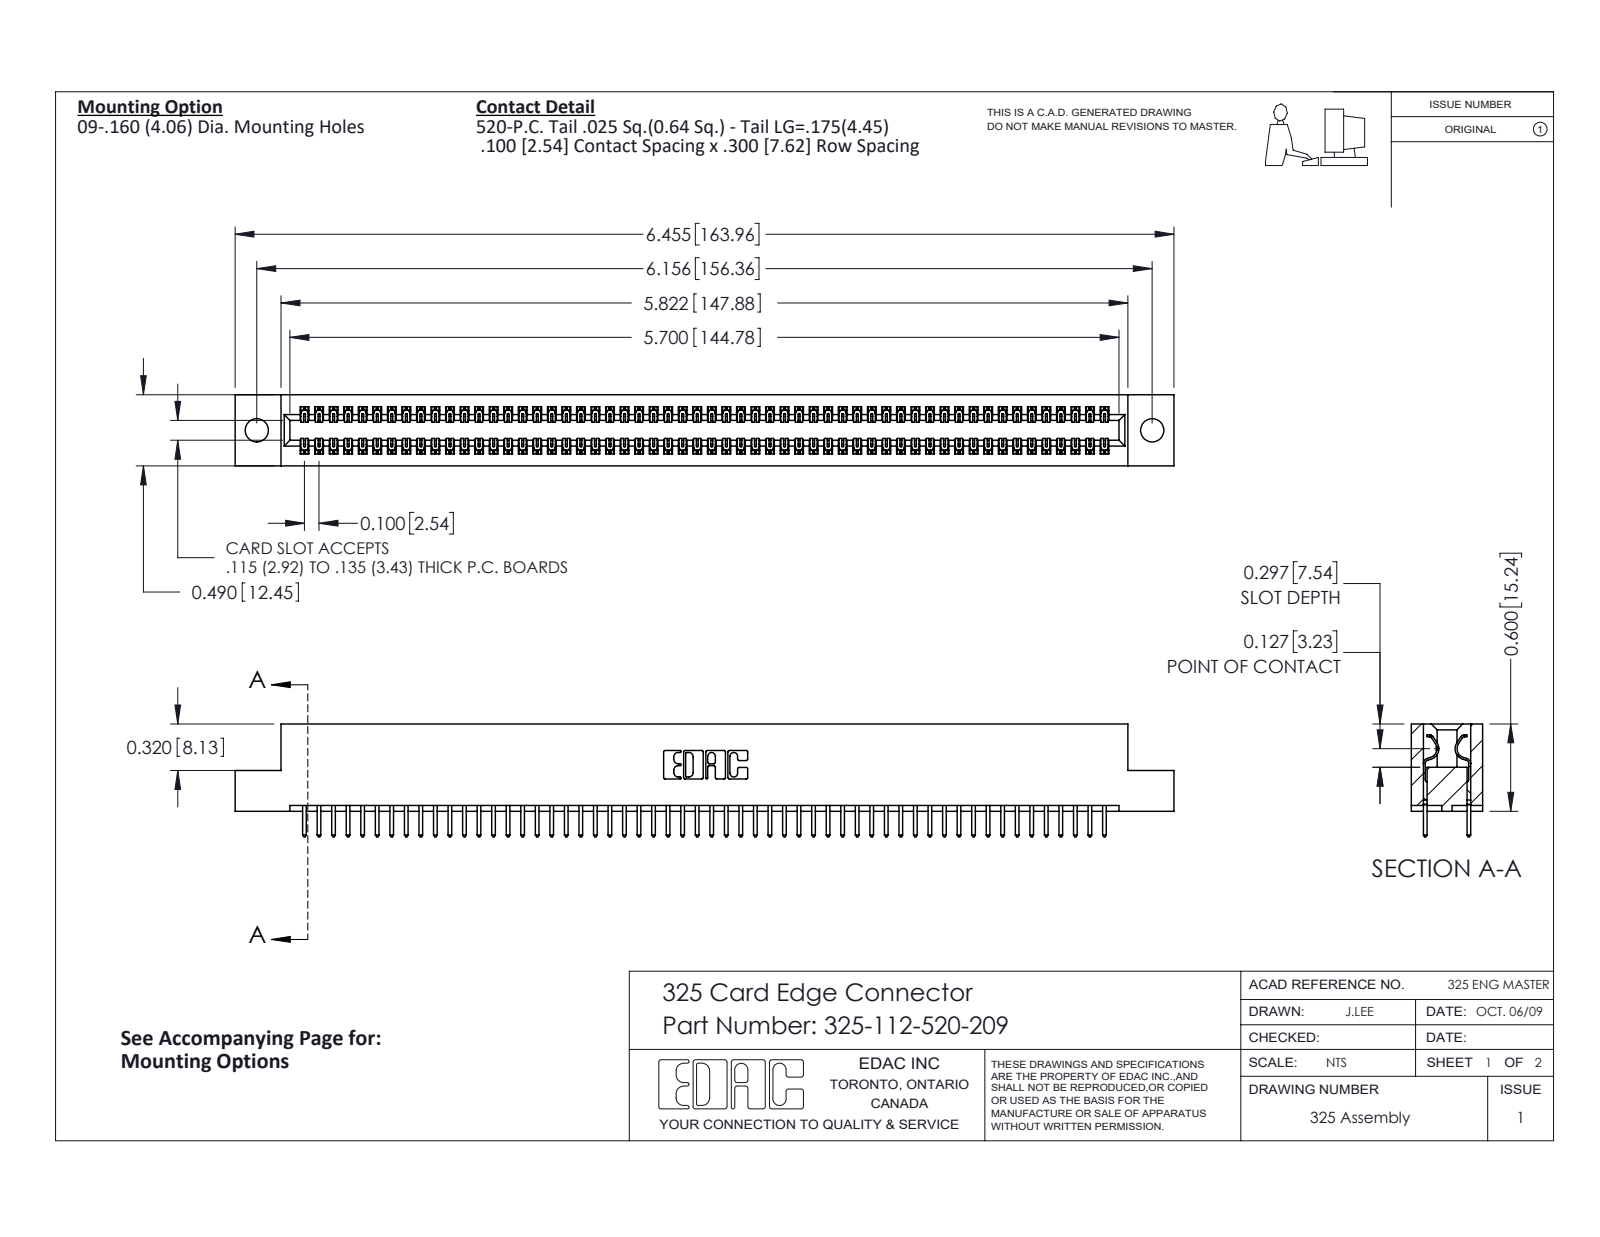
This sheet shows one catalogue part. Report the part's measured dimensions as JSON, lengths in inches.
{"part_name": "325 Part_.160 TH; 325-112-520-209; 325-292-001_325-293-120", "step_written_by": "SolidWorks 2016 (CONFIG_CONTROL_DESIGN)", "units": "inches", "bodies": {"solids": 113, "faces": 5938, "planar": 4102, "cylindrical": 1836, "other": 0}, "overall_size": [6.455, 0.775, 0.49], "volume_in3": 1.284, "surface_area_in2": 39.52, "round_holes": [[0.16, 2]], "partial_cylinders_radius": [[0.006, 168], [0.01, 112], [0.01, 22], [0.007, 6], [0.031, 6], [0.026, 3], [0.014, 2], [0.022, 2]], "face_to_face_distances": [0.083, 0.407, 0.49, 0.3, 0.107, 0.383, 0.025, 0.325, 0.275, 0.263], "hole_center_spacings": [6.156]}
